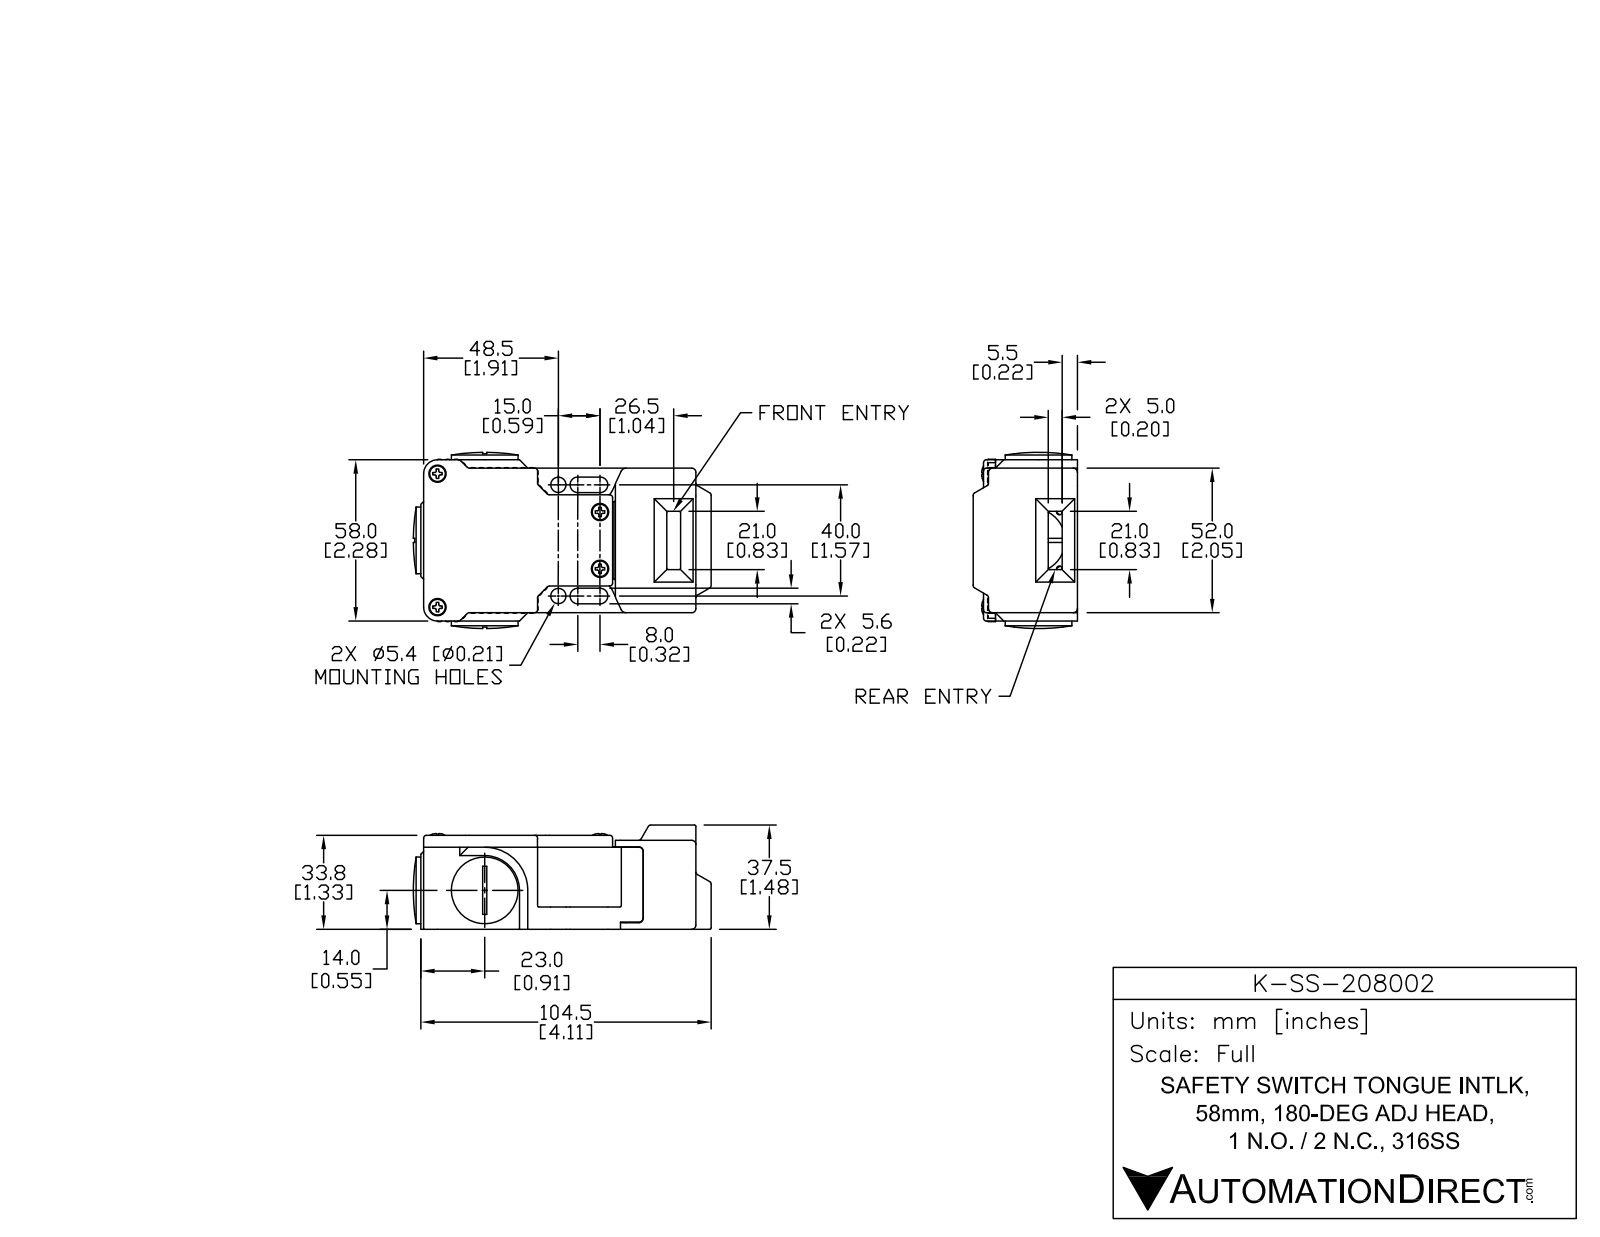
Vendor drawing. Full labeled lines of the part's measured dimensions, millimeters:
Part name (STEP PRODUCT): K-SS-208002
STEP written by: SolidWorks 2013 (AUTOMOTIVE_DESIGN)
Units: millimetres
Bodies: 1 solid, 235 faces (164 planar, 44 cylindrical, 27 other)
Overall size (bounding box): 100.75 × 60.2 × 38
Volume: 159 050 mm³ · Surface area: 27 548 mm²
Round holes (diameter × count): ⌀5.4 ×2, ⌀19.33 ×1, ⌀20 ×1
Round bosses / shafts (diameter × count): ⌀5.6 ×2, ⌀23.8 ×1
Partial cylindrical surfaces — rounded edges, fillets, slot ends (radius × count): R1.5 ×12, R2 ×4, R2.75 ×4, R4 ×3, R5 ×2
Main face-to-face distances: 3, 55, 33.5, 52, 96, 33.45, 58, 1.05, 5, 4.1
Hole centre spacings: 40
